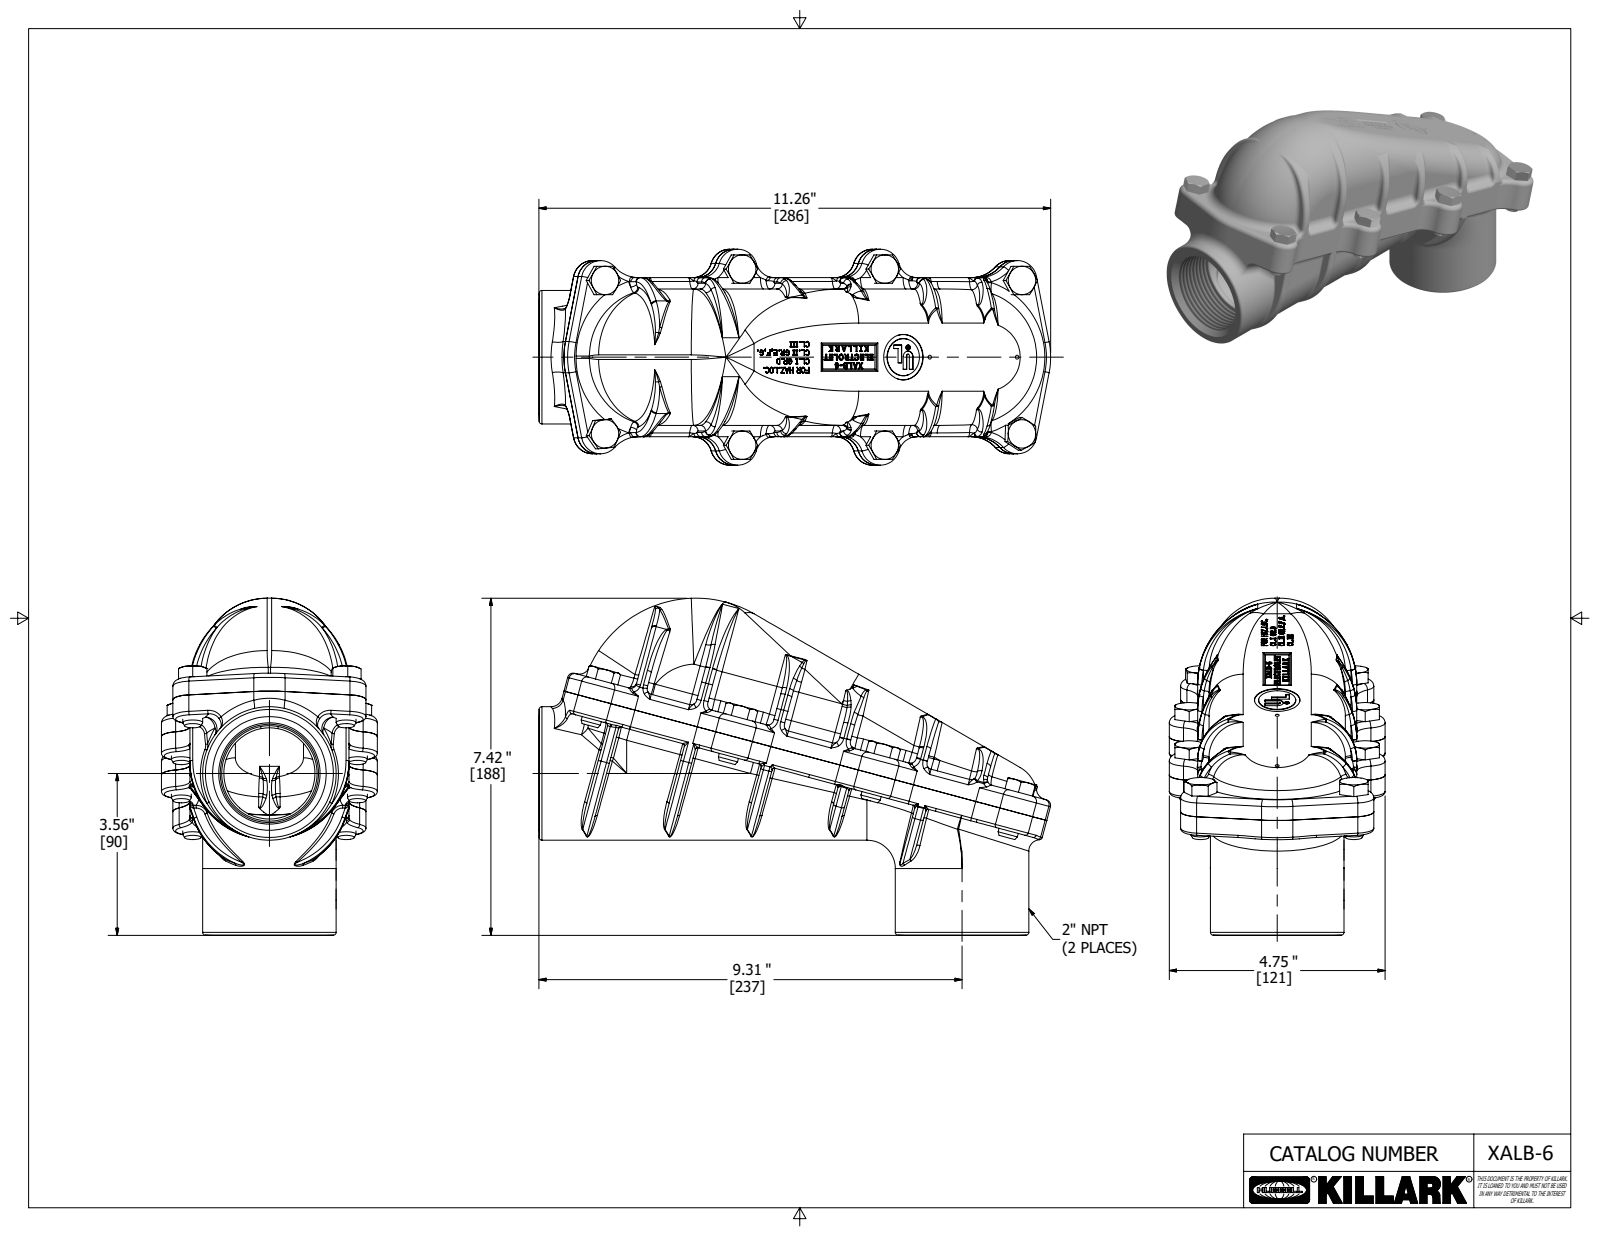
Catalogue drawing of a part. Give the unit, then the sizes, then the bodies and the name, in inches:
Units: inches
Overall size (bounding box): 11.261 × 7.418 × 4.75
Round holes (diameter × count): ⌀0.36 ×8, ⌀0.469 ×8, ⌀0.086 ×2, ⌀2.5 ×1
Round bosses / shafts (diameter × count): ⌀0.563 ×8, ⌀0.437 ×8, ⌀2.937 ×2
Partial cylindrical surfaces — rounded edges, fillets, slot ends (radius × count): R0.062 ×36, R0.125 ×31, R0.437 ×20, R0.031 ×16, R0.094 ×16, R0.05 ×12, R0.25 ×10, R1.25 ×8
Main face-to-face distances: 0.25, 2.5, 3, 0.5, 3.25, 2.75, 3.5, 0.031, 0.438, 0.438
Hole centre spacings: 3.375, 3.875, 4.786, 3.135, 6.38, 7.333, 3.137, 4.787
Volume: 49.48 in³ · Surface area: 364.3 in²
Bodies: 10 solids, 3500 faces (1102 planar, 282 cylindrical, 2116 other)
Part name (STEP PRODUCT): XALB-6; 0240373-2; 0240374-2; ANSI B18.2.1 - 7_16-14 UNC - 1(3)
STEP written by: Autodesk Inventor 2020 (AUTOMOTIVE_DESIGN)
